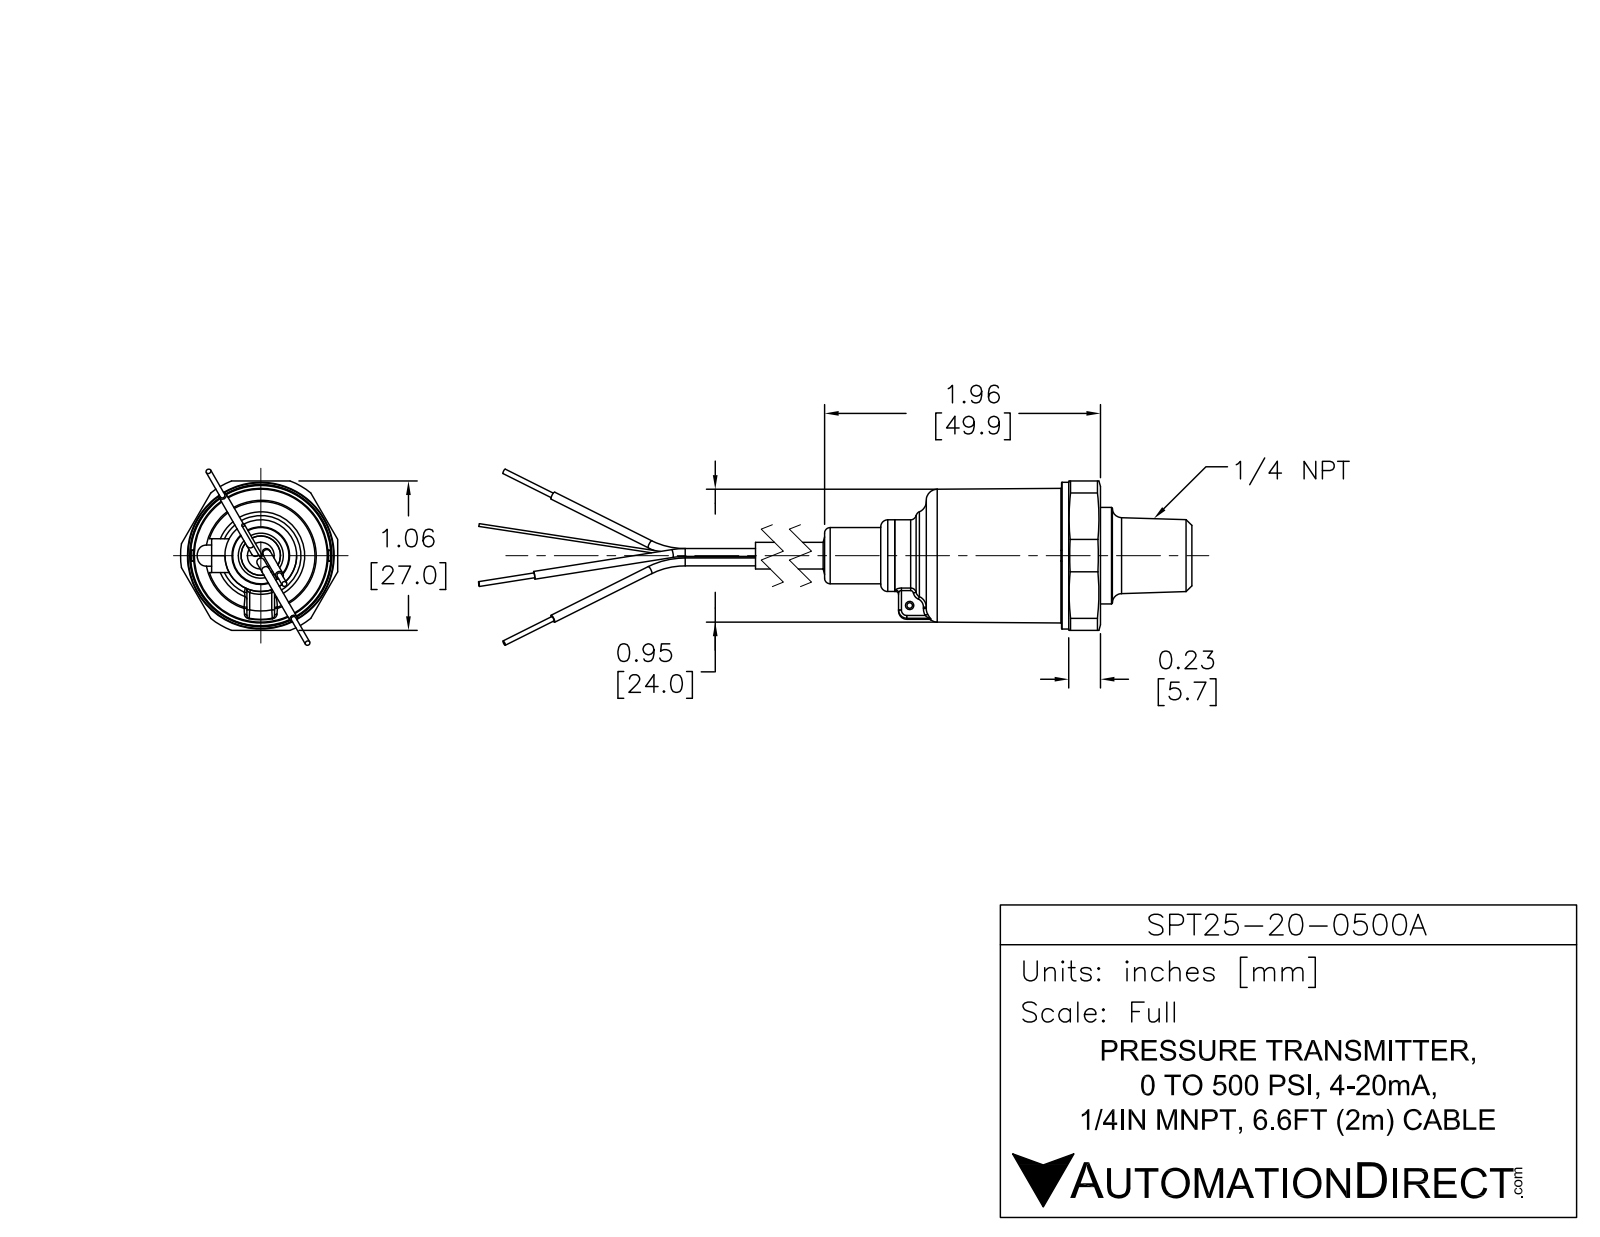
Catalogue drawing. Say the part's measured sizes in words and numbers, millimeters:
The part is named "SPT25-20-0500A". Its 3-D file was written by "SolidWorks 2017 (AUTOMOTIVE_DESIGN)". It is 7 solids with 116 faces: 32 planar, 49 cylindrical and 35 other. Overall it measures 153.3 by 29 by 27.09 millimeters. Its volume is 20 801 cubic millimeters and its surface area 7 170 square millimeters. Round holes: 1 of diameter 1, 1 of diameter 3.3. Round bosses or shafts: 6 of diameter 1.4, 5 of diameter 0.75, 1 of diameter 26.75, 1 of diameter 24, 1 of diameter 17.5, 1 of diameter 14, 1 of diameter 13, 1 of diameter 10. Partial cylindrical surfaces (rounded edges, fillets, slot ends): 1 of radius 2, 1 of radius 14.5. The main face-to-face distances are 6.75, 24, 17.25, 42.75, 49.5, 66.75, 44, 1.25, 5.5, 22.75.
